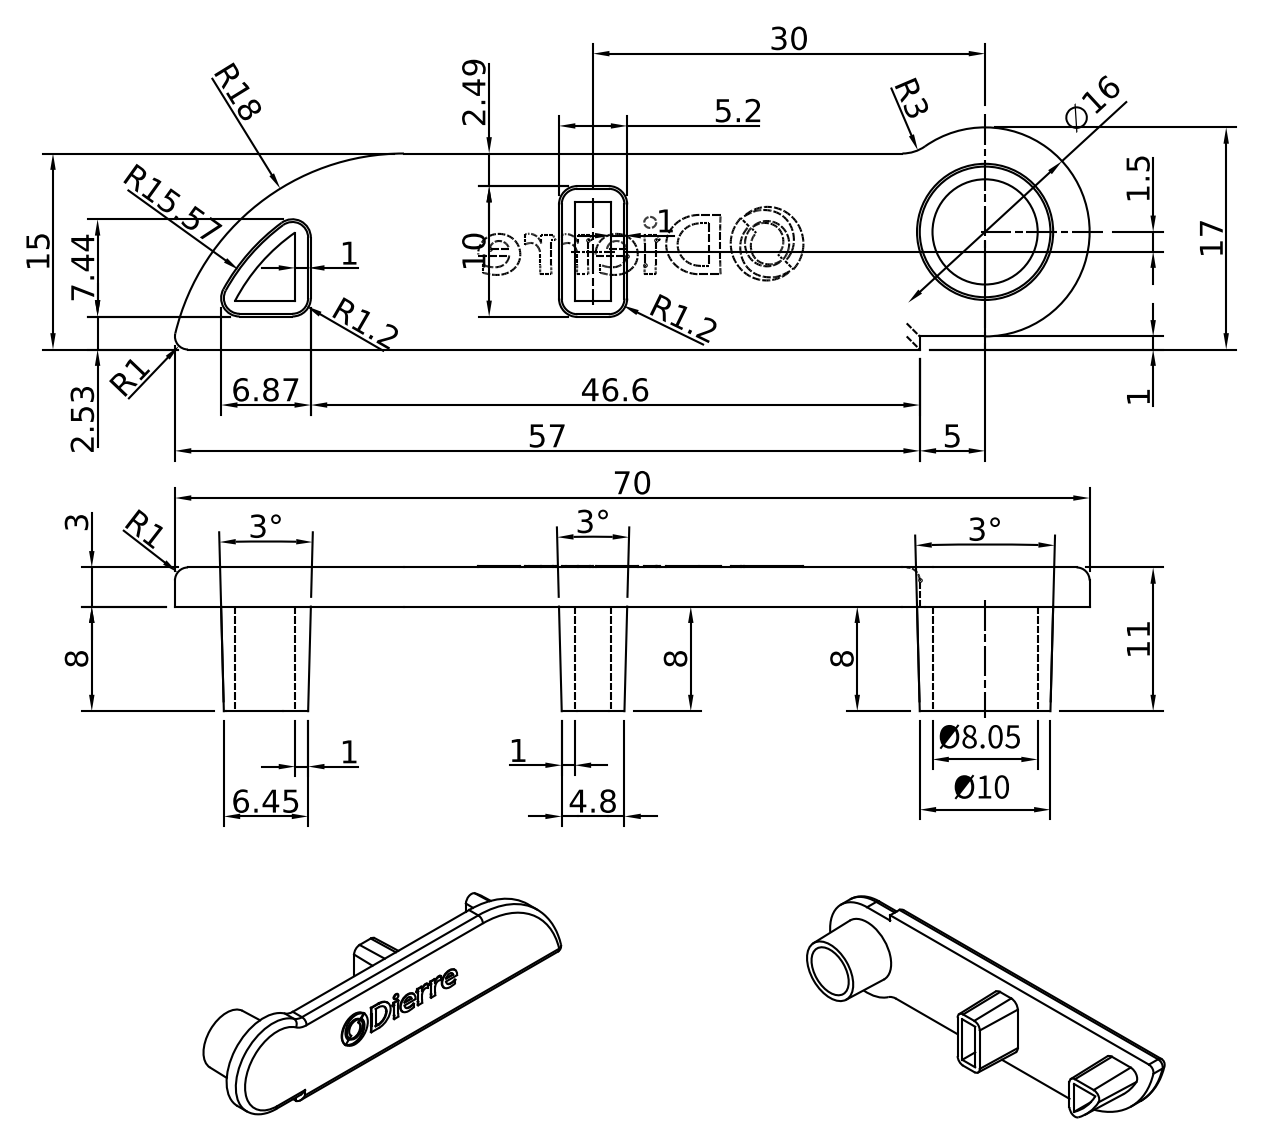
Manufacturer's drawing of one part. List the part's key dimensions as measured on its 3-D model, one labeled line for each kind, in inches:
Part name (STEP PRODUCT): DTPTR0000194
STEP written by: Autodesk Inventor 2019 (AUTOMOTIVE_DESIGN)
Units: inches
Bodies: 1 solid, 135 faces (73 planar, 10 cylindrical, 52 other)
Overall size (bounding box): 2.756 × 0.669 × 0.437
Volume: 0.214 in³ · Surface area: 5.436 in²
Round holes (diameter × count): ⌀0.317 ×1
Partial cylindrical surfaces — rounded edges, fillets, slot ends (radius × count): R0.039 ×5, R0.118 ×1, R0.315 ×1, R0.573 ×1, R0.709 ×1
Main face-to-face distances: 0.118, 0.953, 0.591, 0.433, 0.315, 0.11, 0.146, 0.445, 0.122, 0.437
